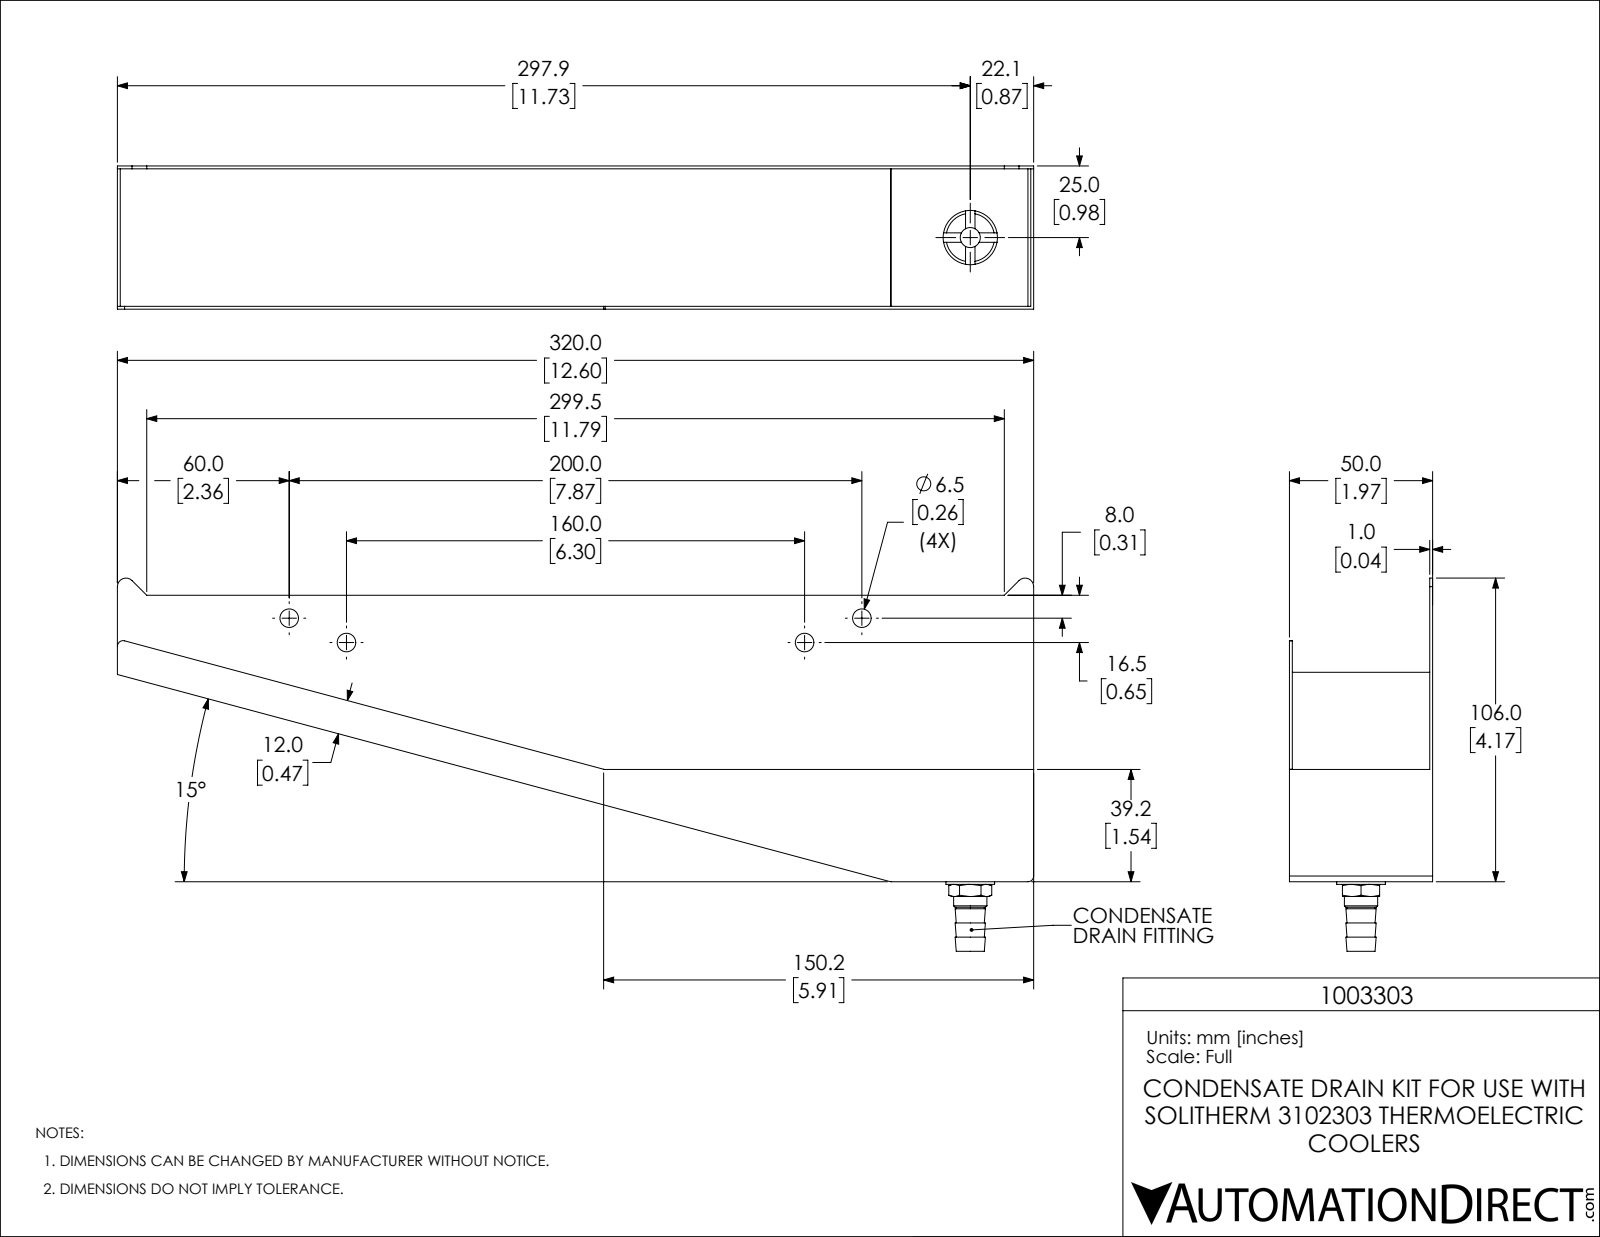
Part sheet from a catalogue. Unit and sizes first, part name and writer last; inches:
Units: inches
Overall size (bounding box): 12.599 × 5.13 × 1.969
Round holes (diameter × count): ⌀0.256 ×4, ⌀0.276 ×1, ⌀0.394 ×1, ⌀0.433 ×1, ⌀0.484 ×1
Round bosses / shafts (diameter × count): ⌀0.746 ×1, ⌀0.669 ×1, ⌀0.457 ×1, ⌀0.387 ×1
Partial cylindrical surfaces — rounded edges, fillets, slot ends (radius × count): R0.079 ×4, R0.039 ×2, R0.118 ×2
Main face-to-face distances: 0.039, 1.929, 1.969, 1.89, 3.937, 3.898, 1.543, 1.504, 2.394, 0.433
Hole centre spacings: 0.856, 7.094, 6.299, 7.874
Volume: 2.958 in³ · Surface area: 149.7 in²
Bodies: 4 solids, 92 faces (49 planar, 20 cylindrical, 23 other)
Part name (STEP PRODUCT): 1003303
STEP written by: SolidWorks 2019 (AUTOMOTIVE_DESIGN)
